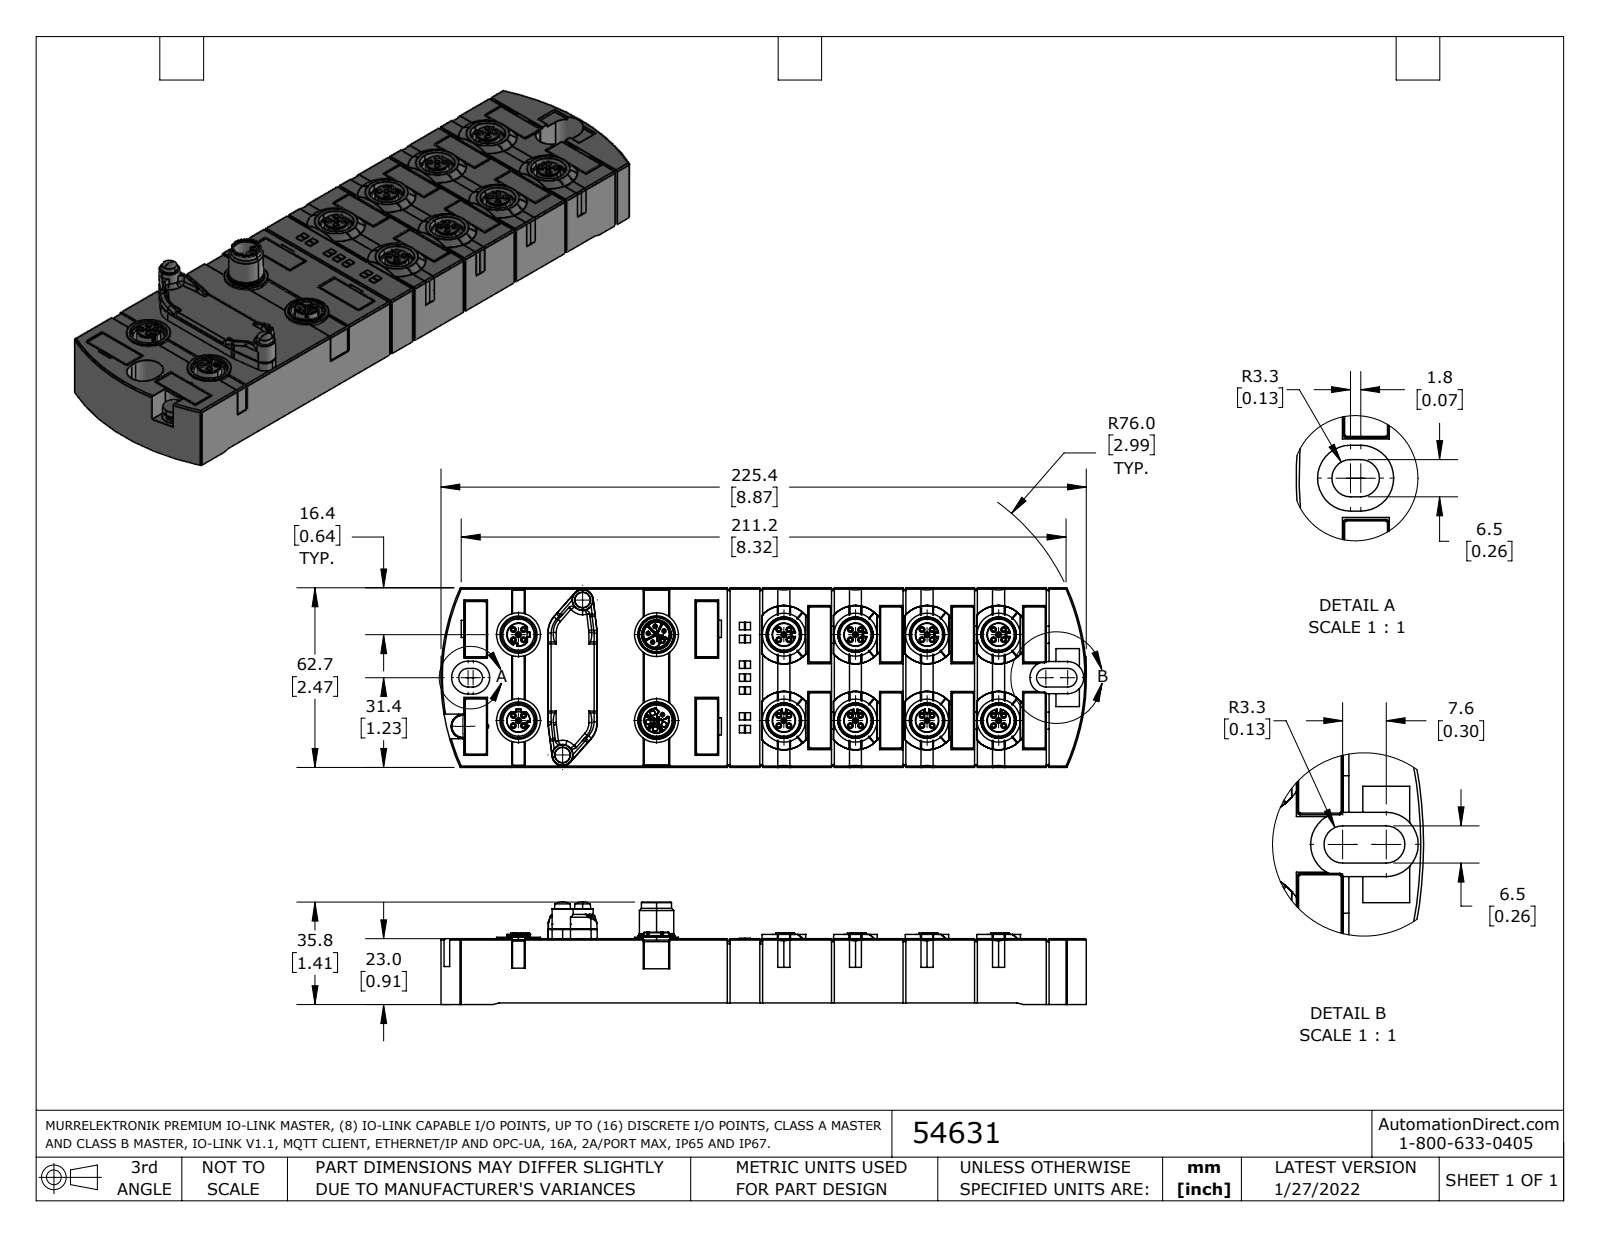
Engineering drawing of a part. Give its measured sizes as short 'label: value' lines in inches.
name: 54631
written by: SolidWorks 2021 (AUTOMOTIVE_DESIGN)
unit: in
bodies: 2 solids, 2068 faces (734 planar, 668 cylindrical, 666 other)
size: 8.874 × 2.469 × 1.413
volume: 18.87 in³; area: 85.23 in²
holes: 50× ⌀0.047, 9× ⌀0.43, 4× ⌀0.065, 2× ⌀0.512, 1× ⌀0.128, 1× ⌀0.161, 1× ⌀0.35, 1× ⌀0.43, 1× ⌀0.43
bosses: 50× ⌀0.079, 10× ⌀0.323, 5× ⌀0.059, 4× ⌀0.602, 2× ⌀0.516, 2× ⌀0.289, 1× ⌀0.484, 1× ⌀0.472
rounds: 64× R0.02, 21× R0.039, 20× R0.01, 15× R0.008, 14× R0.006, 13× R0.004, 12× R0.394, 10× R0.012
face distances: 0.882, 2.469, 0.024, 0.906, 0.904, 0.88, 0.02, 0.217, 0.059, 0.199
hole spacings: 0.139, 1.181, 0.098, 1.969, 3.65, 3.836, 0.196, 0.984
